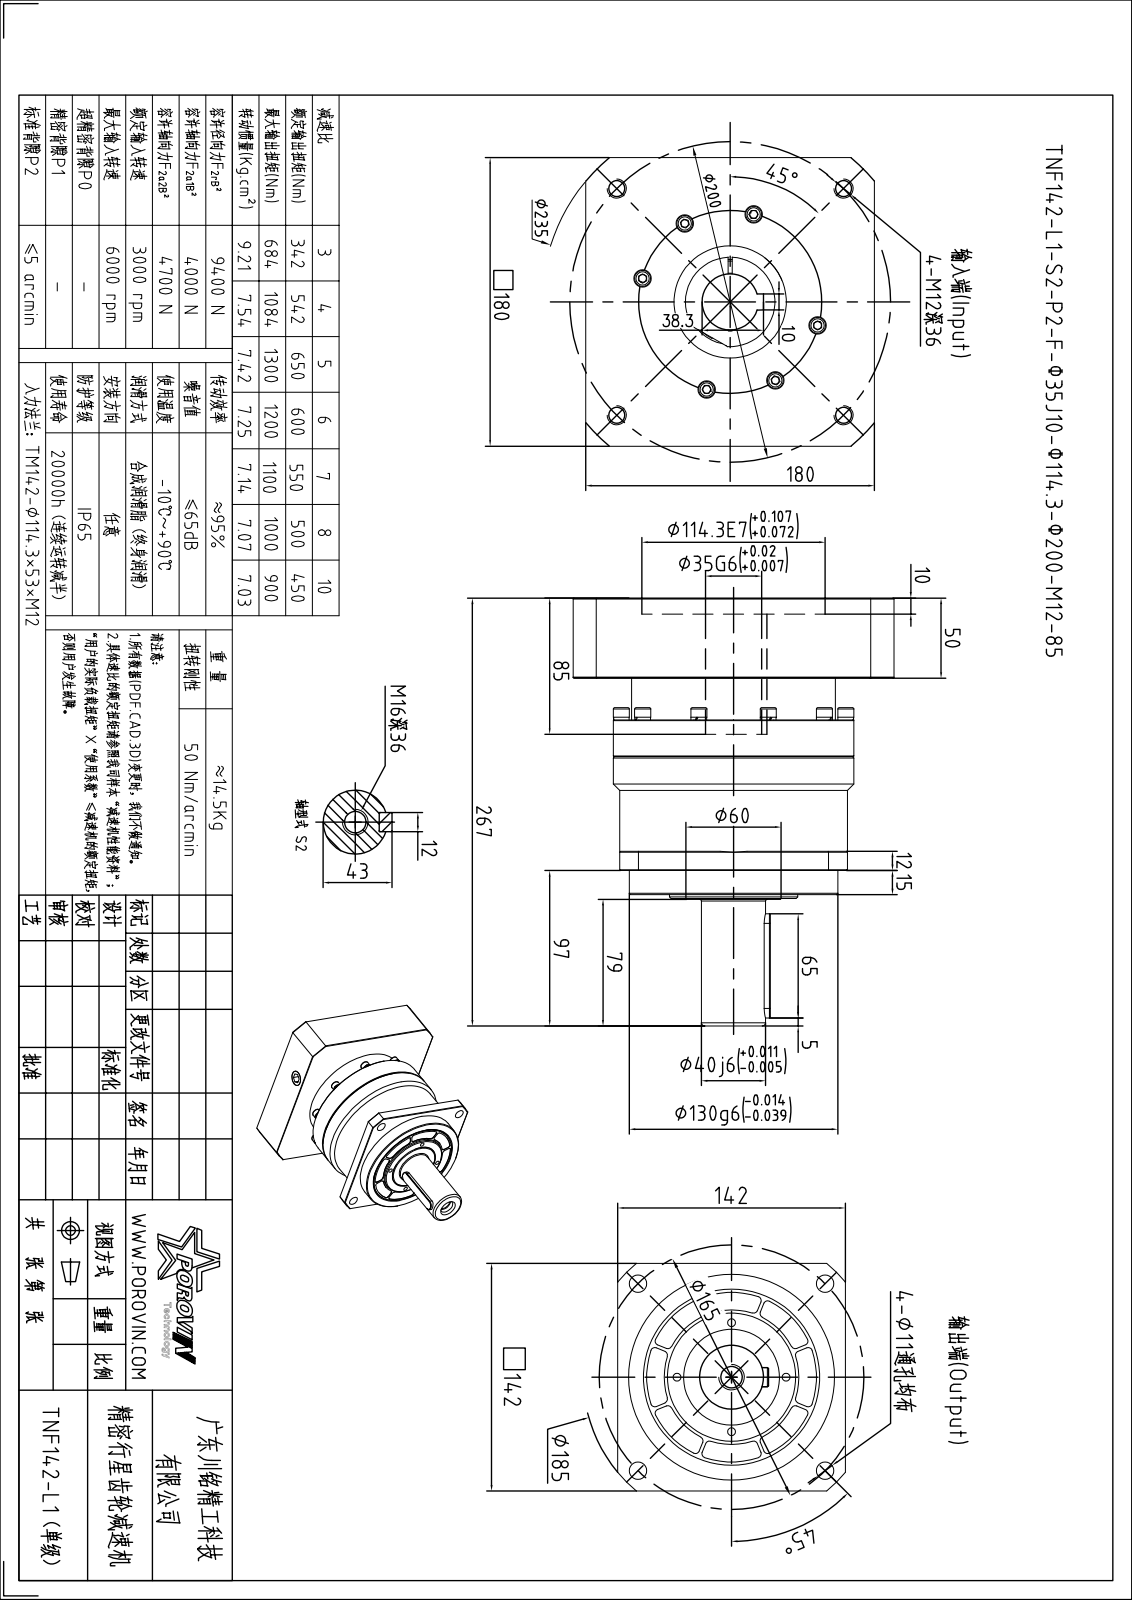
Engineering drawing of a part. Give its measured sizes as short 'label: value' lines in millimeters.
name: 输入轴KB142D35键10外形图; hexagon socket head cap screws gb_GB_FASTENER_SCREWS_HSHCS M10X35-N; hex socket set screws with flat point gb_GB_FASTENER_SCREWS_HSFP M16X16-N; hexagon socket head cap screws gb_GB_FASTENER_SCREWS_HSHCS M8X30-N (+4 more)
written by: SolidWorks 2016 (CONFIG_CONTROL_DESIGN)
unit: mm
bodies: 39 solids, 1056 faces (460 planar, 381 cylindrical, 215 other)
size: 267 × 180 × 180
volume: 3 431 000 mm³; area: 342 473 mm²
holes: 10× ⌀6.6, 10× ⌀6.68, 6× ⌀6.8, 6× ⌀8.68, 6× ⌀9, 6× ⌀14, 5× ⌀11, 4× ⌀5, 4× ⌀10.2, 1× ⌀8.5, 1× ⌀13.6, 1× ⌀17
bosses: 11× ⌀10, 10× ⌀9.88, 10× ⌀6, 6× ⌀13, 6× ⌀12.88, 6× ⌀8, 2× ⌀16, 1× ⌀150
rounds: 32× R2, 2× R6, 1× R9, 1× R42.5, 1× R51, 1× R56, 1× R57.15, 1× R92.5
face distances: 50, 99, 49, 3, 52, 47, 180, 26, 138, 71
hole spacings: 70, 43.26, 62.84, 79.22, 82.29, 110.07, 127.18, 129.64
